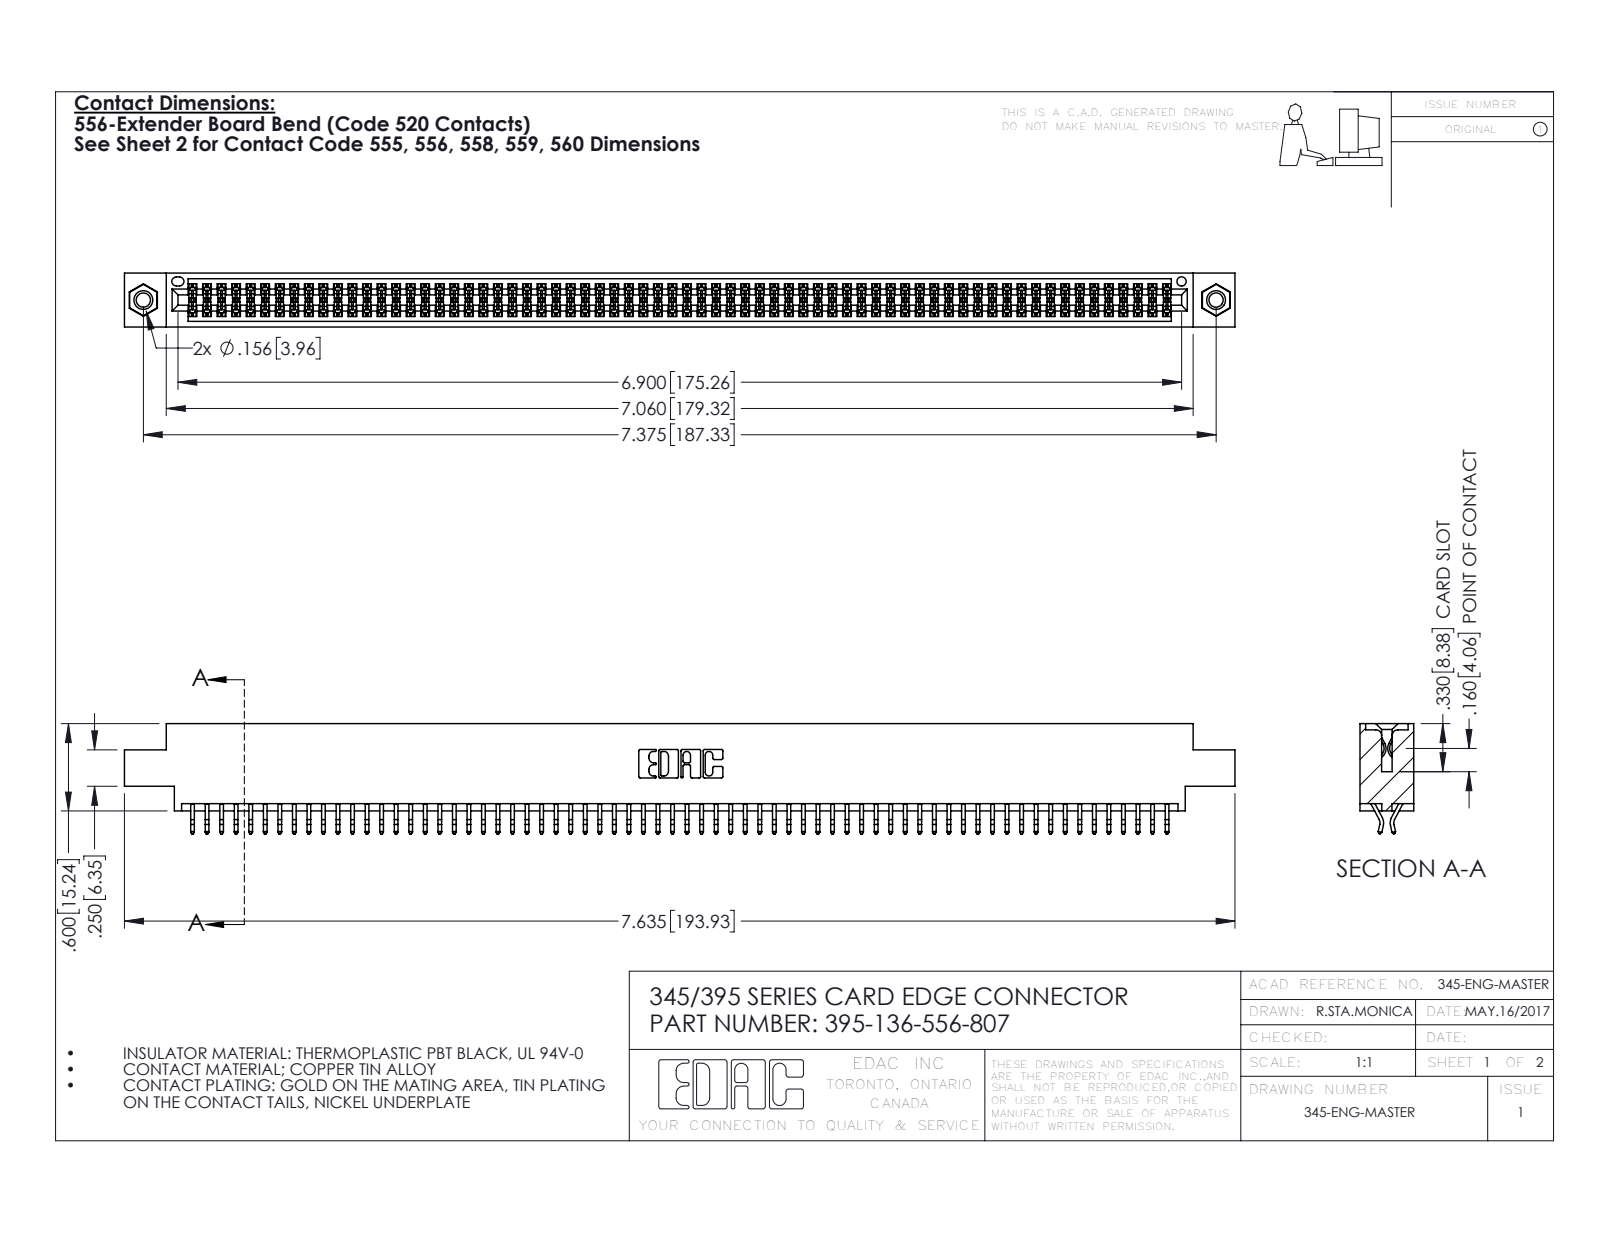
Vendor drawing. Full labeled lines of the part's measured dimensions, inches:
Part name (STEP PRODUCT): 345-292-001_556 Tail; 345-250-001_345-250-005-103; 395-136-556-807; 345 Part_0.170 Offset - 0.156 Dia-TI
STEP written by: SolidWorks 2016 (CONFIG_CONTROL_DESIGN)
Units: inches
Bodies: 139 solids, 7806 faces (5148 planar, 2642 cylindrical, 16 other)
Overall size (bounding box): 7.635 × 0.757 × 0.37
Volume: 1.156 in³ · Surface area: 44.27 in²
Round holes (diameter × count): ⌀0.098 ×2, ⌀0.125 ×2, ⌀0.156 ×2, ⌀0.064 ×1
Round bosses / shafts (diameter × count): ⌀0.155 ×2
Partial cylindrical surfaces — rounded edges, fillets, slot ends (radius × count): R0.006 ×204, R0.01 ×22, R0.007 ×6, R0.031 ×6, R0.026 ×3, R0.01 ×2, R0.014 ×2, R0.019 ×2
Main face-to-face distances: 0.072, 0.298, 0.37, 0.2, 0.025, 0.098, 0.272, 0.225, 0.175, 0.149
Hole centre spacings: 0.27, 7.139, 7.375
